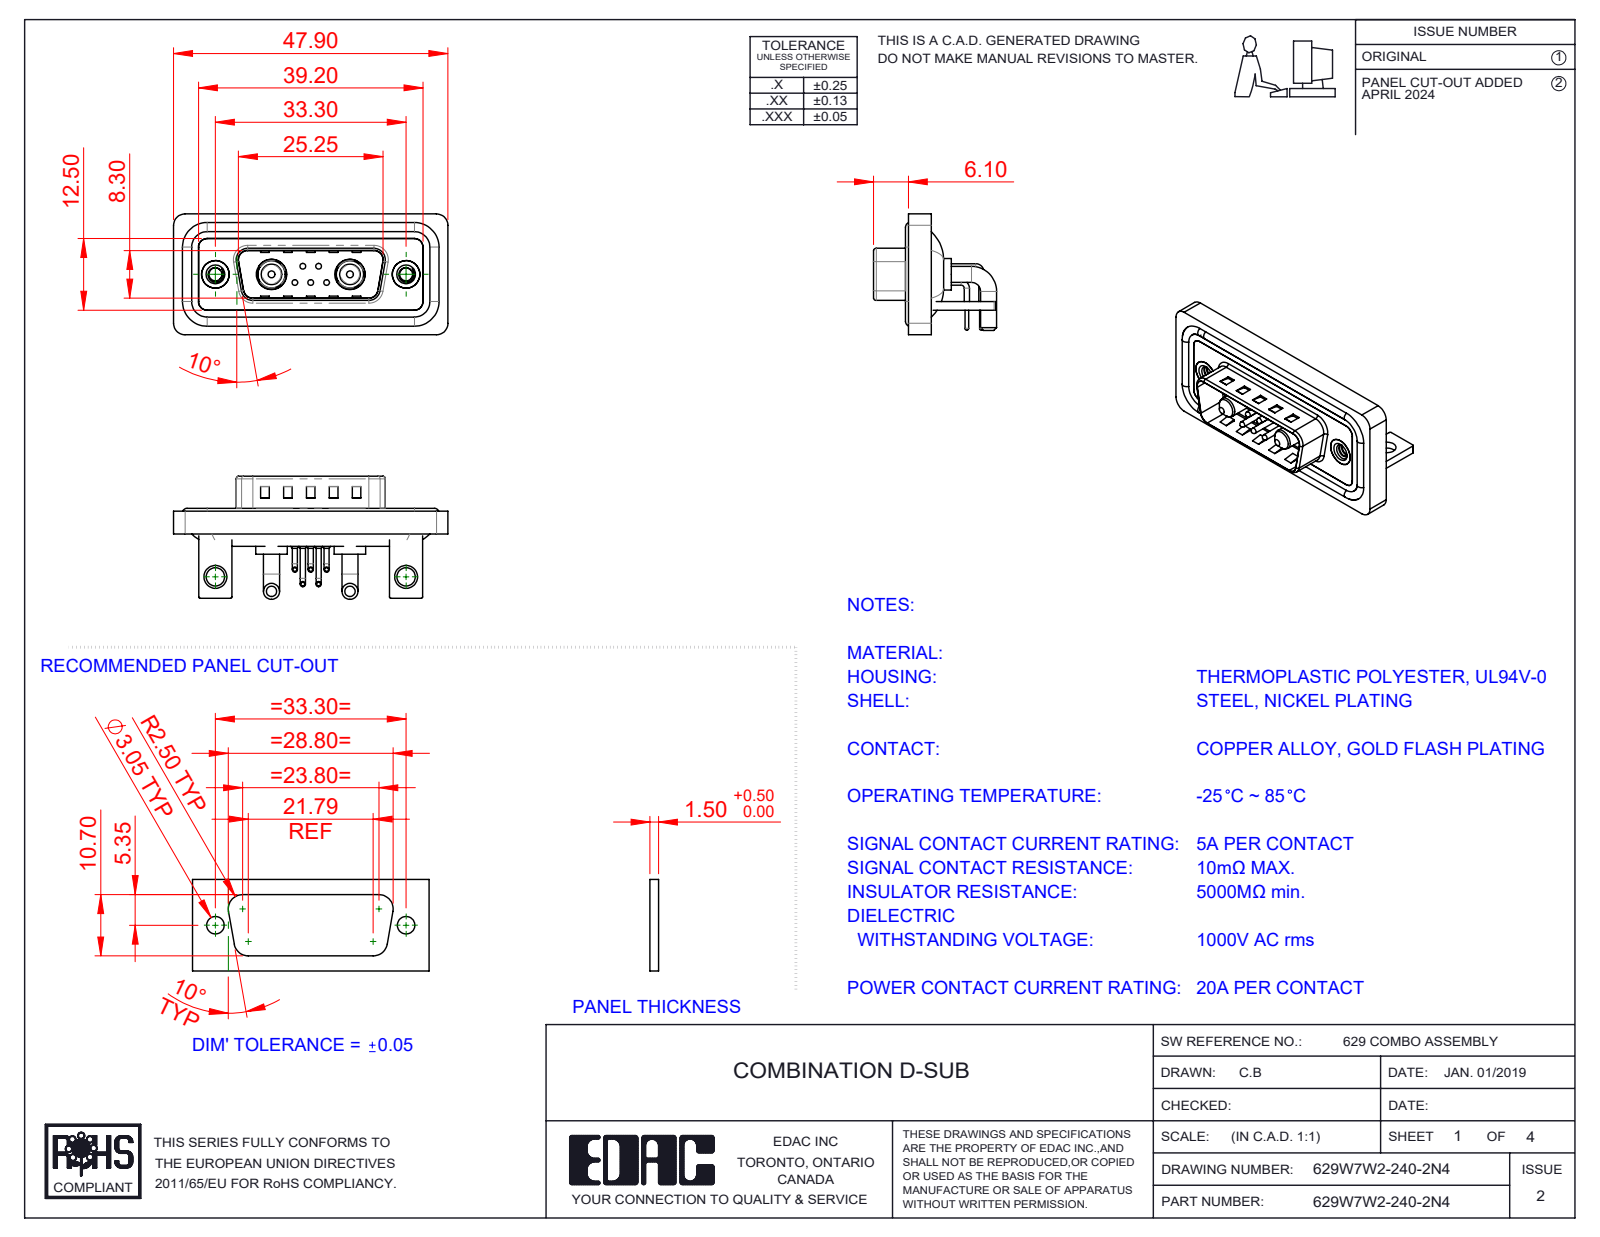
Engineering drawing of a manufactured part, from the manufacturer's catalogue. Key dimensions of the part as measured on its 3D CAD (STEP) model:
Part name (STEP PRODUCT): 629W7W2-140-2N4; 629Combo Stabilizer Bracket; 629Combo Contact Row 1; 629Combo Housing_7W2 (+6 more)
STEP written by: SolidWorks 2023 (CONFIG_CONTROL_DESIGN)
Units: millimetres
Bodies: 18 solids, 1123 faces (537 planar, 424 cylindrical, 162 other)
Overall size (bounding box): 47.9 × 21.5 × 21.1
Volume: 5 958 mm³ · Surface area: 9 727 mm²
Round holes (diameter × count): ⌀0.75 ×5, ⌀1.6 ×5, ⌀2 ×5, ⌀2.26 ×2, ⌀3.2 ×2, ⌀4 ×2, ⌀4.8 ×2, ⌀4.85 ×2, ⌀5 ×2, ⌀5.3 ×2
Round bosses / shafts (diameter × count): ⌀0.9 ×10, ⌀1.5 ×5, ⌀1 ×5, ⌀0.65 ×5, ⌀2.8 ×4, ⌀1.6 ×4, ⌀5.5 ×2, ⌀5.2 ×2
Partial cylindrical surfaces — rounded edges, fillets, slot ends (radius × count): R2 ×21, R1.5 ×18, R0.25 ×16, R0.5 ×9, R1.6 ×8, R1.01 ×5, R0.6 ×4, R0.65 ×4
Main face-to-face distances: 0.4, 1.5, 0.8, 2.9, 2.1, 1.1, 1.6, 1.2, 3.7, 4.5
Hole centre spacings: 3.16, 2.77, 9.8, 23.5, 33.3, 4.31, 4.33, 5.03
